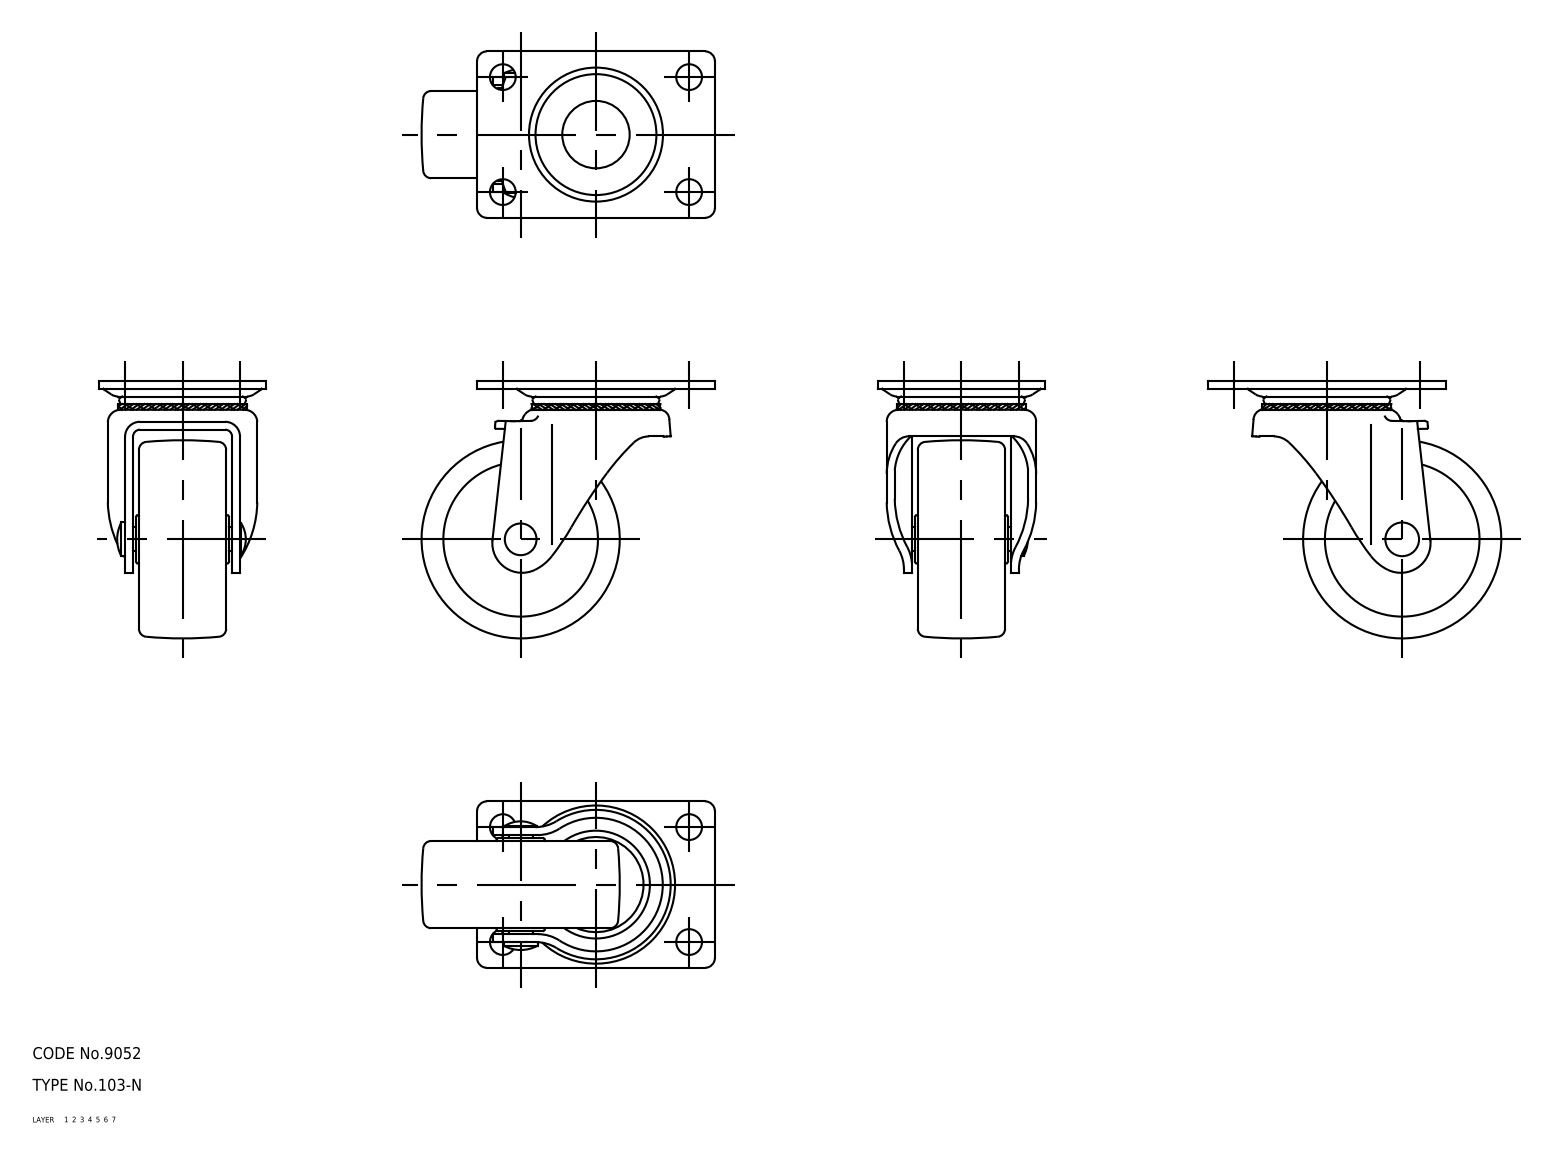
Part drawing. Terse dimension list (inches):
name: wheel; mounting plate; main shaft; axle (+1 more)
written by: CADfix (AUTOMOTIVE_DESIGN)
unit: in
bodies: 5 solids, 210 faces (0 planar, 0 cylindrical, 210 other)
size: 2.913 × 2.559 × 1.654
volume: 2.607 in³; area: 38.06 in²
